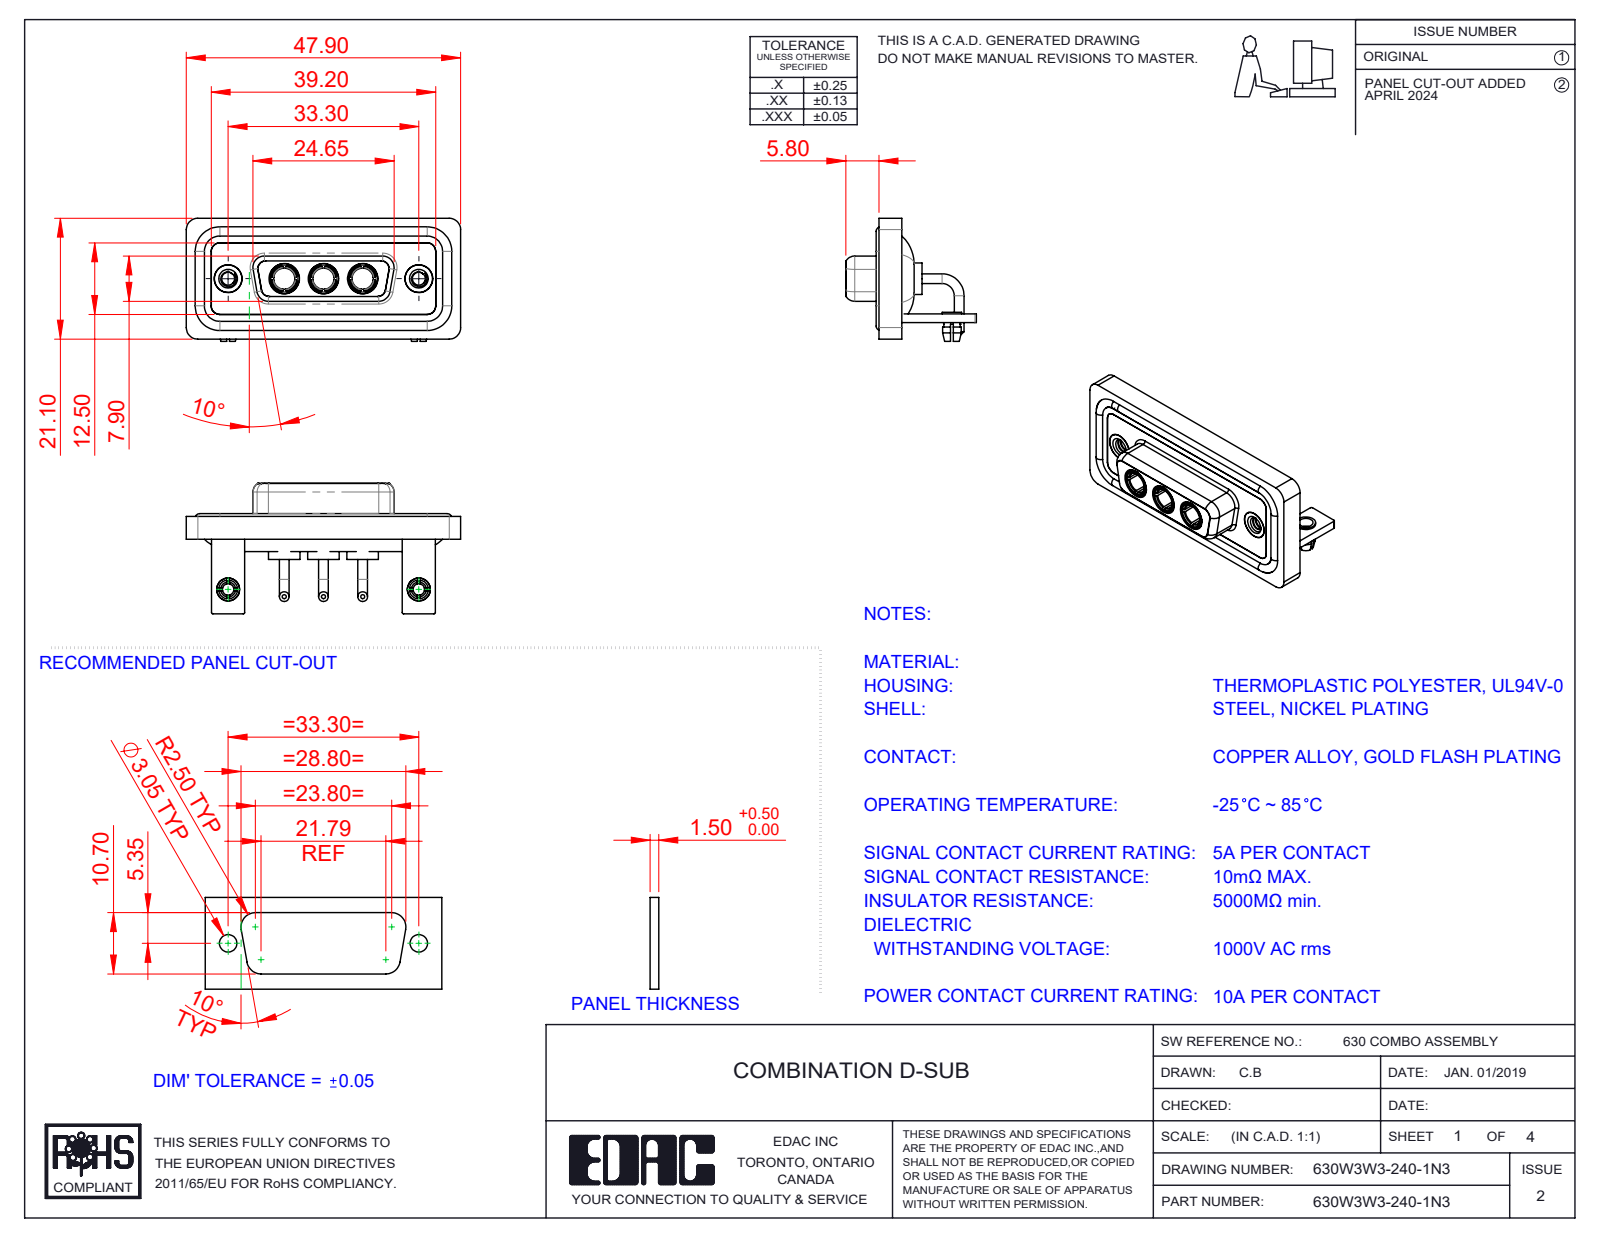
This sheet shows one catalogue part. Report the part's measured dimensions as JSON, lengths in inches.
{"part_name": "630Combo Board Lock_50 Contacts; 630W3W3-240-1N3; Power Socket_10A RA; 630Combo Shell Rear_15 Contacts (+5 more)", "step_written_by": "SolidWorks 2023 (CONFIG_CONTROL_DESIGN)", "units": "inches", "bodies": {"solids": 17, "faces": 760, "planar": 260, "cylindrical": 319, "other": 181}, "overall_size": [1.886, 0.898, 0.846], "volume_in3": 0.391, "surface_area_in2": 16.69, "round_holes": [[0.191, 5], [0.146, 3], [0.209, 3], [0.079, 2], [0.089, 2], [0.098, 2], [0.126, 2], [0.157, 2], [0.159, 2], [0.197, 2]], "round_bosses_or_shafts": [[0.067, 6], [0.063, 4], [0.217, 3], [0.205, 3], [0.195, 3], [0.187, 3], [0.148, 3], [0.195, 2]], "partial_cylinders_radius": [[0.079, 21], [0.059, 18], [0.01, 16], [0.053, 12], [0.063, 8], [0.02, 5], [0.024, 4], [0.026, 4]], "face_to_face_distances": [0.016, 0.114, 0.059, 0.071, 0.146, 0.043, 0.161, 0.063, 0.098, 0.055], "hole_center_spacings": [0.27, 0.386, 0.656, 0.925, 1.311, 0.539]}
